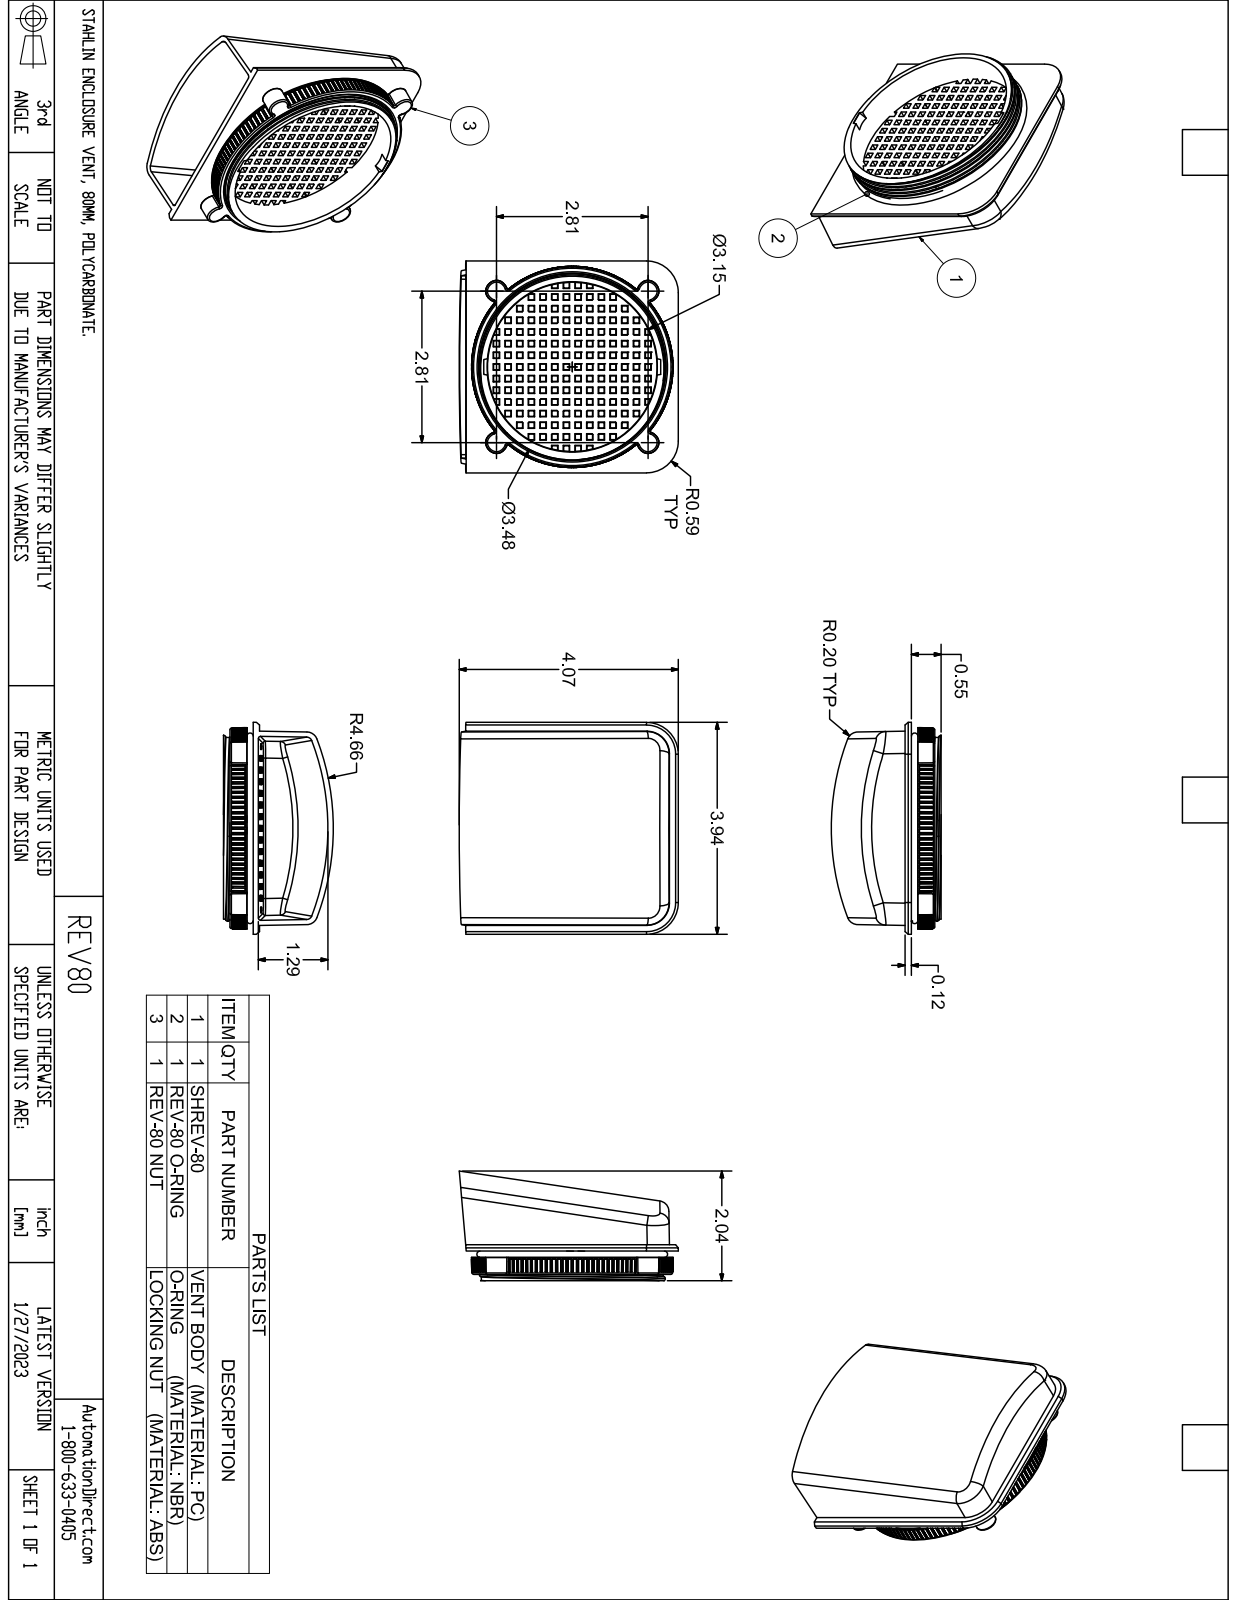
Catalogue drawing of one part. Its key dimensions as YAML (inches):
part_name: "REAH-V80"
step_written_by: "SolidWorks 2019 (AUTOMOTIVE_DESIGN)"
units: inches
bodies: {solids: 3, faces: 2094, planar: 900, cylindrical: 490, other: 704}
overall_size: [4.067, 3.937, 2.038]
volume: 5.463
surface_area: 106.1
round_bosses_or_shafts:
  - {diameter: 3.414, count: 1}
partial_cylinders:
  - {radius: 0.078, count: 20}
  - {radius: 0.039, count: 3}
  - {radius: 0.315, count: 2}
  - {radius: 0.413, count: 2}
  - {radius: 0.591, count: 2}
face_to_face_distances: [0.433, 0.216, 0.649, 0.865, 1.081, 0.217, 1.514, 0.118, 1.298, 1.947]
